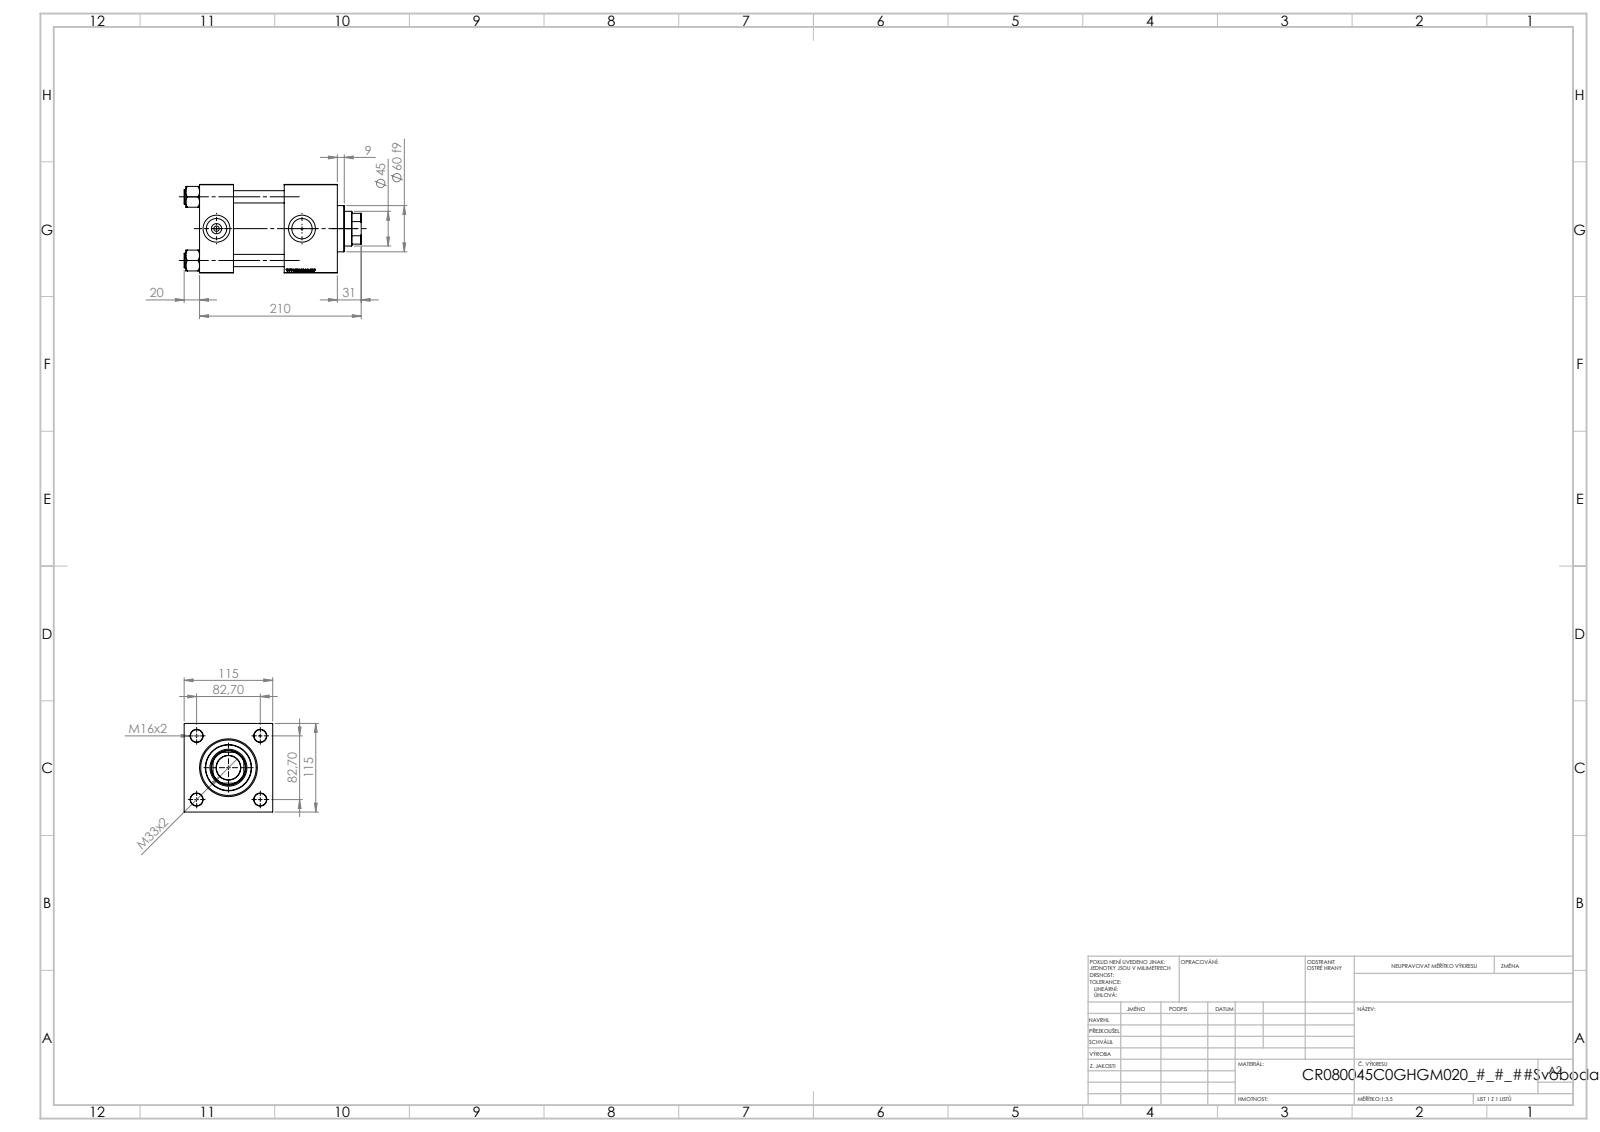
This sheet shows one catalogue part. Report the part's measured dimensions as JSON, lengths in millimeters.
{"part_name": "V215_VC_A; V215CR_C_TYCINKA; NUT_M5_C; V215CR_C_Body (+1 more)", "step_written_by": "SolidWorks 2019 (CONFIG_CONTROL_DESIGN)", "units": "millimeters", "bodies": {"solids": 11, "faces": 1196, "planar": 574, "cylindrical": 86, "other": 536}, "overall_size": [230, 115, 115], "volume_mm3": 1819000, "surface_area_mm2": 273876, "round_holes": [[16, 4], [7, 2], [26.44, 2], [35, 2], [31.5, 1], [45, 1], [48, 1], [61, 1], [72, 1], [80, 1]], "round_bosses_or_shafts": [[19, 4], [86, 1], [60, 1]], "partial_cylinders_radius": [[22, 1]], "face_to_face_distances": [115, 44, 110, 179, 135, 66, 69, 20, 150.3, 106.3], "hole_center_spacings": [58.48, 82.7, 116.96, 111]}
